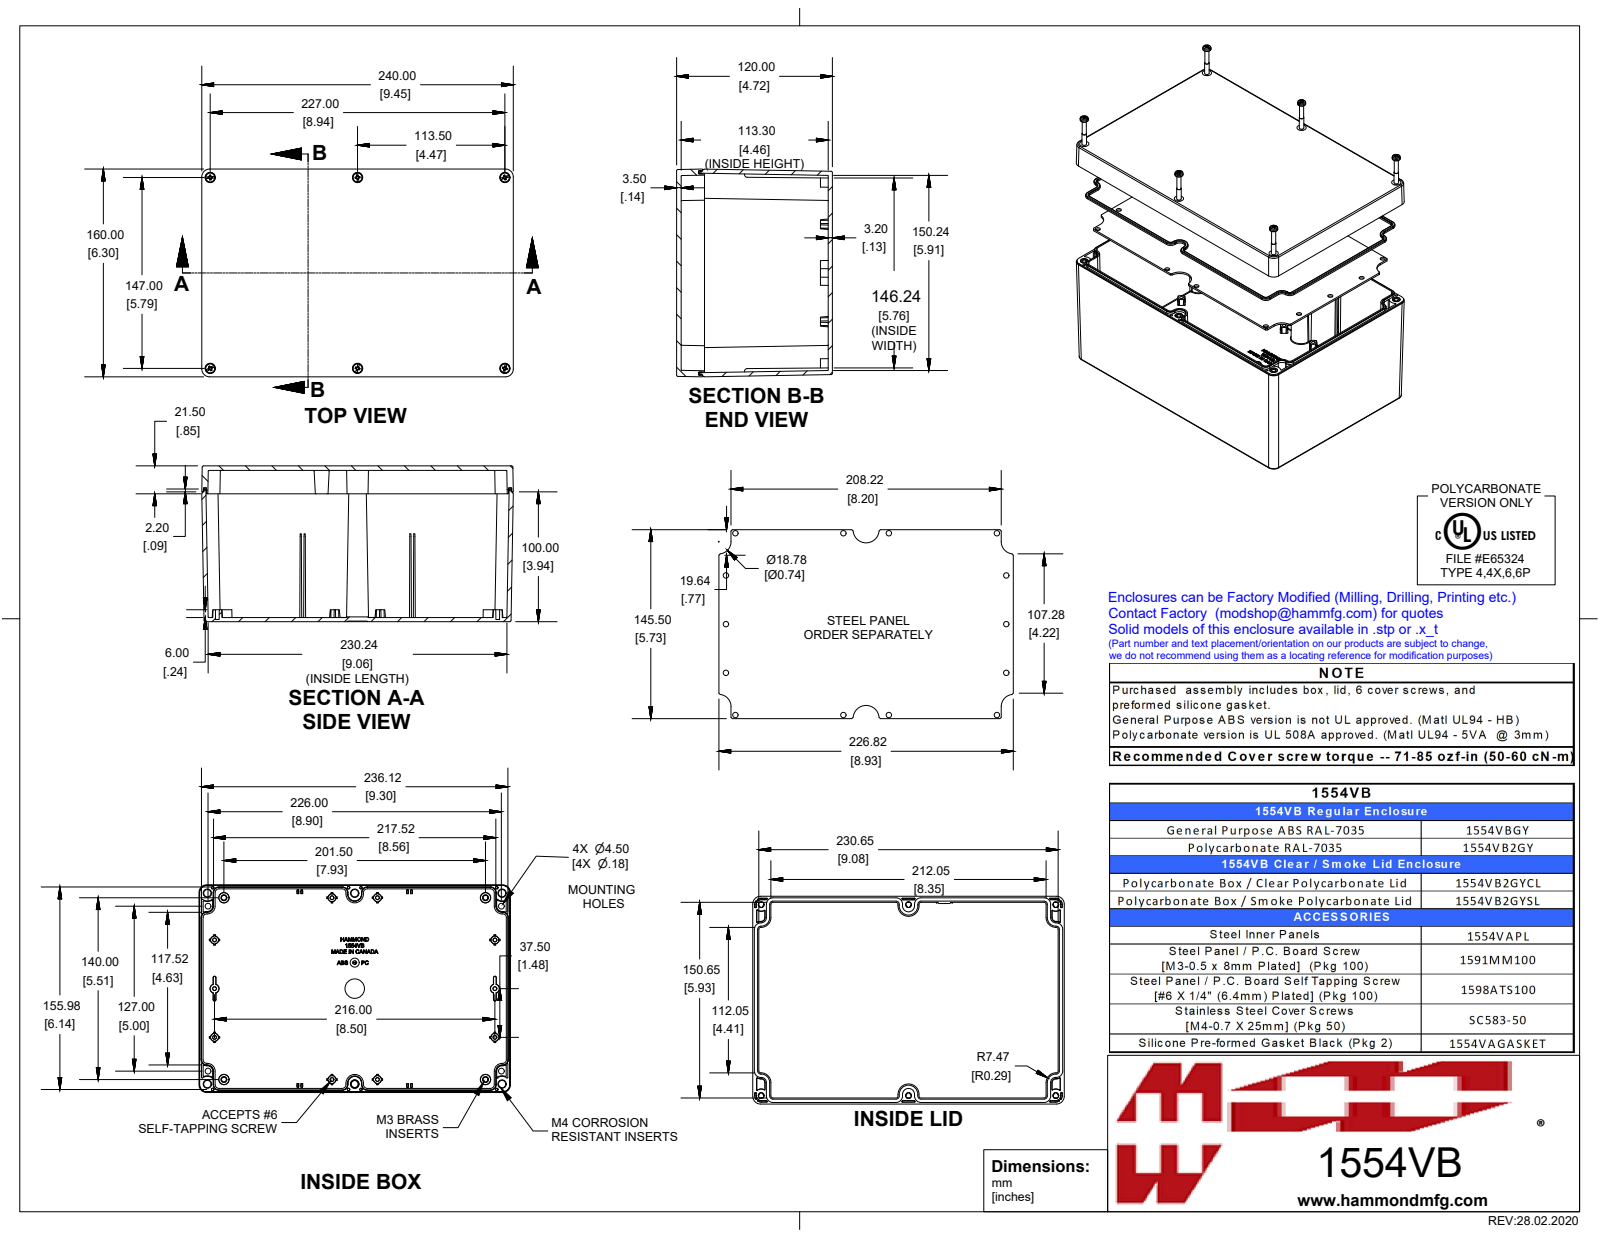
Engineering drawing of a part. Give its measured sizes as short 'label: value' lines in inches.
name: 1554VBGY
written by: SolidWorks 2019 (AUTOMOTIVE_DESIGN)
unit: in
bodies: 20 solids, 2516 faces (1068 planar, 479 cylindrical, 969 other)
size: 9.449 × 6.299 × 4.724
volume: 39.1 in³; area: 713.4 in²
holes: 14× ⌀0.165, 6× ⌀0.128, 5× ⌀0.221, 5× ⌀0.256, 4× ⌀0.097, 1× ⌀0.276, 1× ⌀0.591
bosses: 6× ⌀0.272, 6× ⌀0.25, 6× ⌀0.218, 6× ⌀0.21, 6× ⌀0.152, 6× ⌀0.137, 4× ⌀0.19, 4× ⌀0.154
rounds: 41× R0.02, 28× R0.012, 12× R0.1, 12× R0.195, 8× R0.039, 8× R0.168, 8× R0.236, 4× R0.059
face distances: 0.126, 4.724, 4.587, 0.138, 0.059, 0.236, 4.461, 0.362, 4.598, 4.224
hole spacings: 0.52, 0.703, 1.311, 1.434, 1.476, 2.77, 2.841, 2.902
